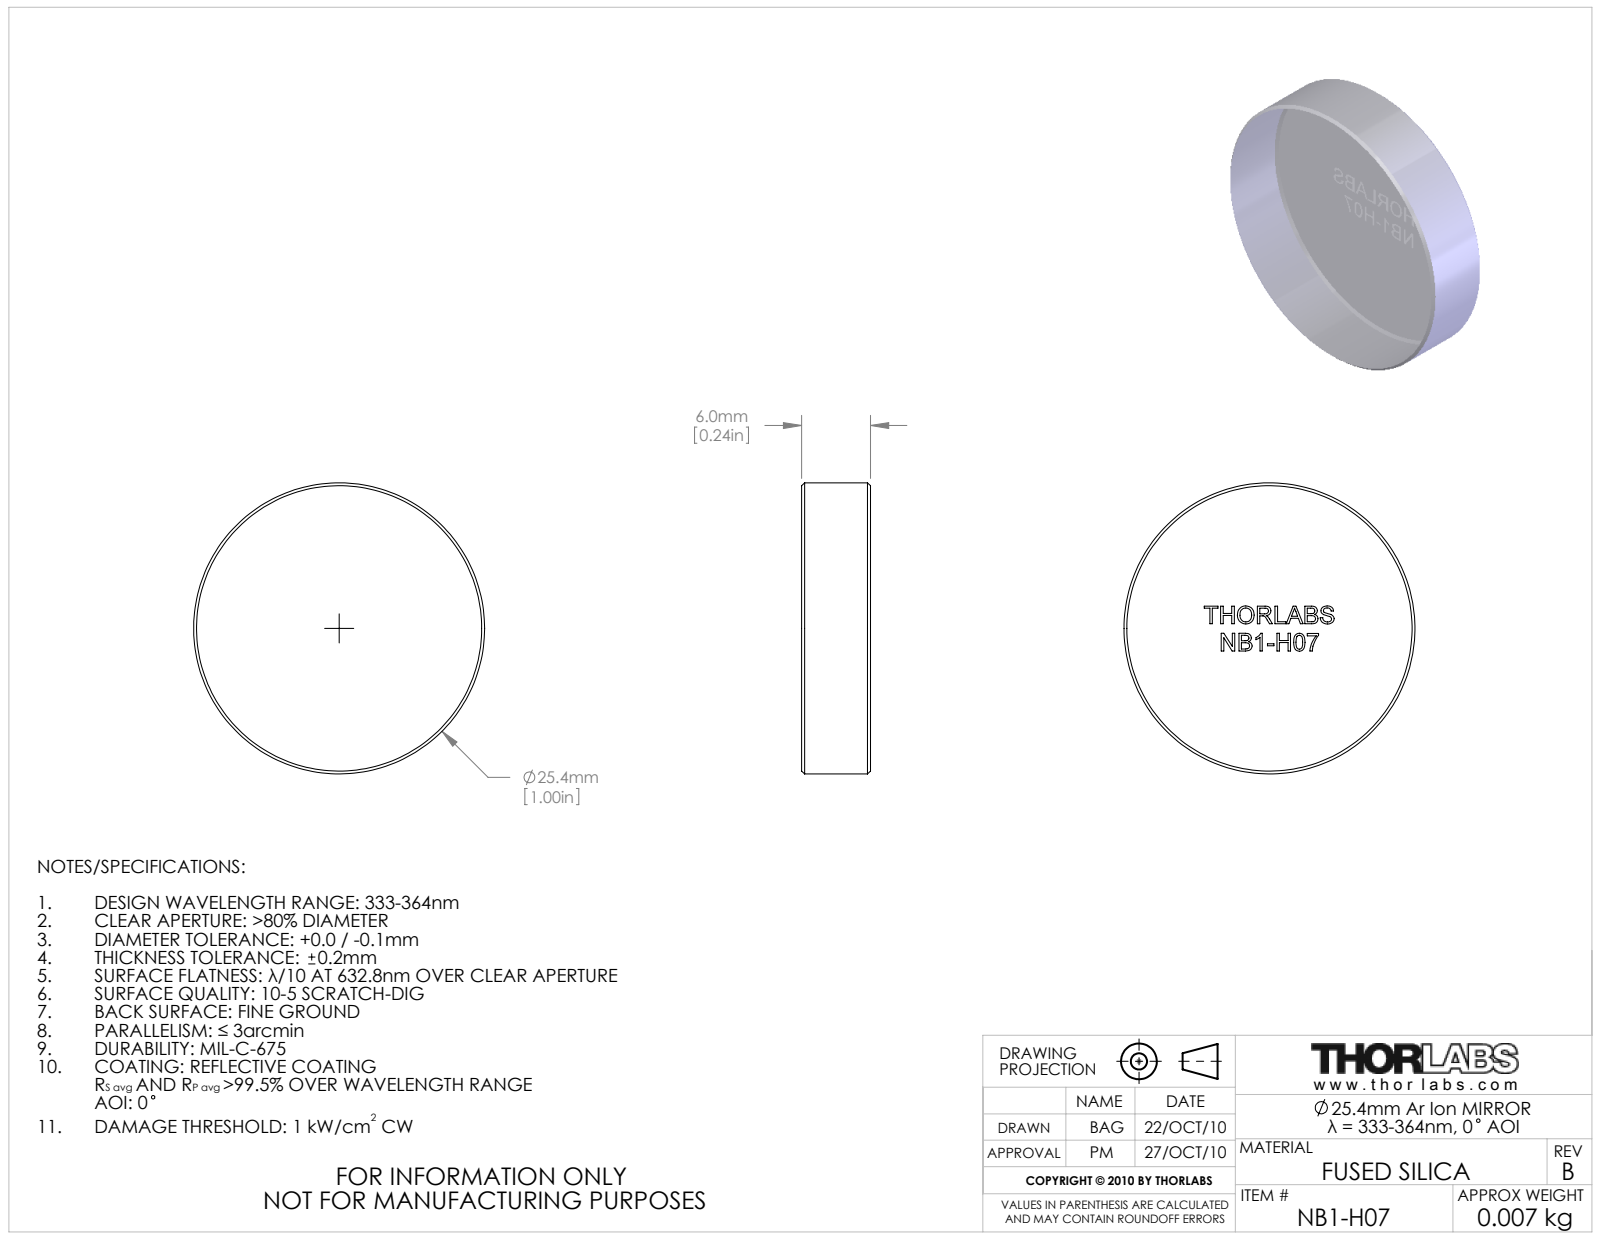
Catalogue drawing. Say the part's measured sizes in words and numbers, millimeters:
The part is named "5367-E0W". Its 3-D file was written by "SolidWorks 2009 (AUTOMOTIVE_DESIGN)". It is 1 solid with 202 faces: 129 planar, 2 cylindrical and 71 other. Overall it measures 25.4 by 25.4 by 6 millimeters. Its volume is 3 030 cubic millimeters and its surface area 1 468 square millimeters. Round bosses or shafts: 1 of diameter 25.4. The main face-to-face distances are 6, 1.5, 4.9, 2.4, 1, 2.4, 2.2, 1.4, 1.1, 1.2.
